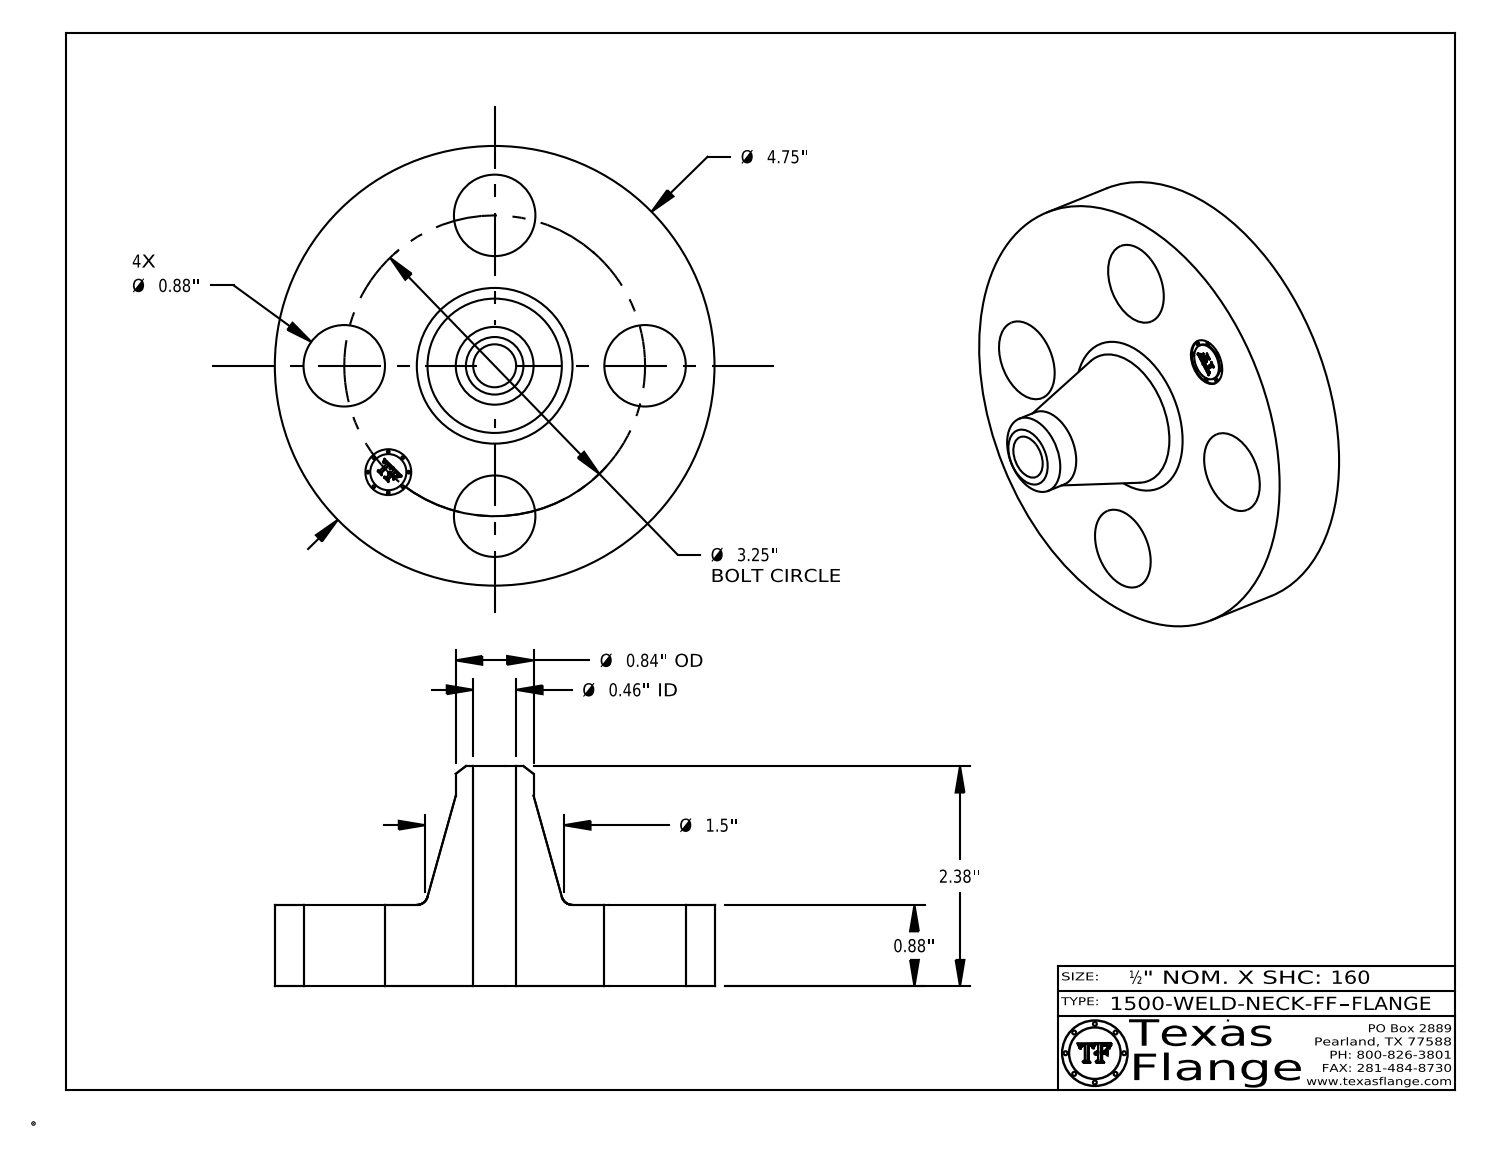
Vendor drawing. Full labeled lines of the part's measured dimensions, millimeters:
Part name (STEP PRODUCT): 1500-WELD-NECK-FF
STEP written by: CATIA V5 STEP AP214 (AUTOMOTIVE_DESIGN)
Units: millimetres
Bodies: 1 solid, 408 faces (368 planar, 34 cylindrical, 6 other)
Overall size (bounding box): 120.7 × 120.7 × 60.5
Volume: 238 100 mm³ · Surface area: 39 050 mm²
Round holes (diameter × count): ⌀22.4 ×4, ⌀11.8 ×1, ⌀12.6 ×1
Round bosses / shafts (diameter × count): ⌀0.8 ×8, ⌀120.7 ×1, ⌀21.3 ×1, ⌀9.9 ×1
Main face-to-face distances: 22.4, 60.5, 38.1, 22, 0.4, 38.5, 3.8, 3.7, 0.7, 2.4
Hole centre spacings: 41.3, 58.4, 31.6, 76.3, 82.6
